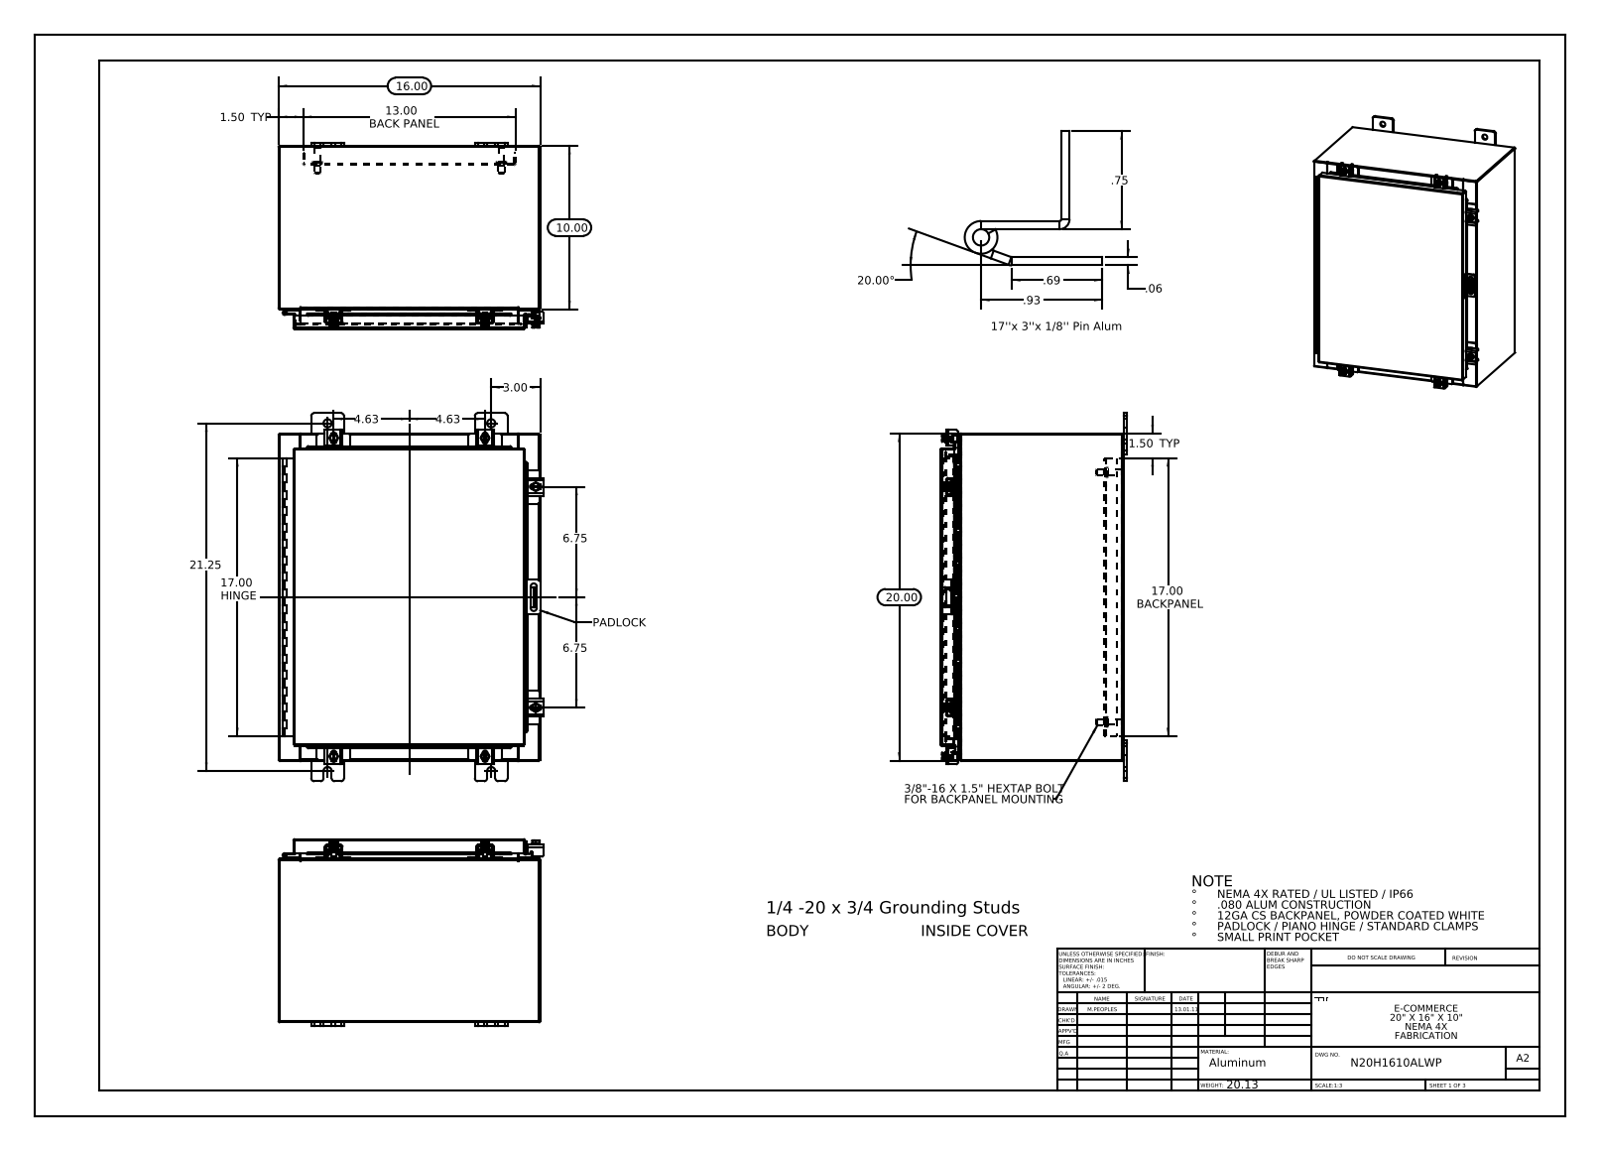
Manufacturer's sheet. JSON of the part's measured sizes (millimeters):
{"part_name": "N20H1610ALWP Backpanel; N20H1610ALWP Mounting Studs; N20H1610ALWP Clamp Top; N20H1610ALWP Padlock Hasp (+8 more)", "step_written_by": "SolidWorks 2013 (CONFIG_CONTROL_DESIGN)", "units": "millimeters", "bodies": {"solids": 47, "faces": 1613, "planar": 860, "cylindrical": 657, "other": 96}, "overall_size": [571.5, 411.8, 289.3], "volume_mm3": 2396000, "surface_area_mm2": 2401000, "round_holes": [[12.7, 8], [5.4, 6], [6.6, 6], [3.2, 2], [3.2, 1]], "round_bosses_or_shafts": [[6.4, 7], [12.7, 6], [10.1, 6], [15.9, 4], [9.5, 4], [8.4, 4]], "partial_cylinders_radius": [[1.5, 30], [0.3, 25], [4.8, 24], [2.2, 21], [3, 12], [3.6, 12], [3.2, 10], [1.3, 9]], "face_to_face_distances": [1.9, 282.6, 404.5, 506.1, 284.5, 280.7, 2.6, 25.4, 27.3, 255.3], "hole_center_spacings": [441.5, 47.2, 57.8, 59.1, 59.1, 77.9, 109.1, 235]}
